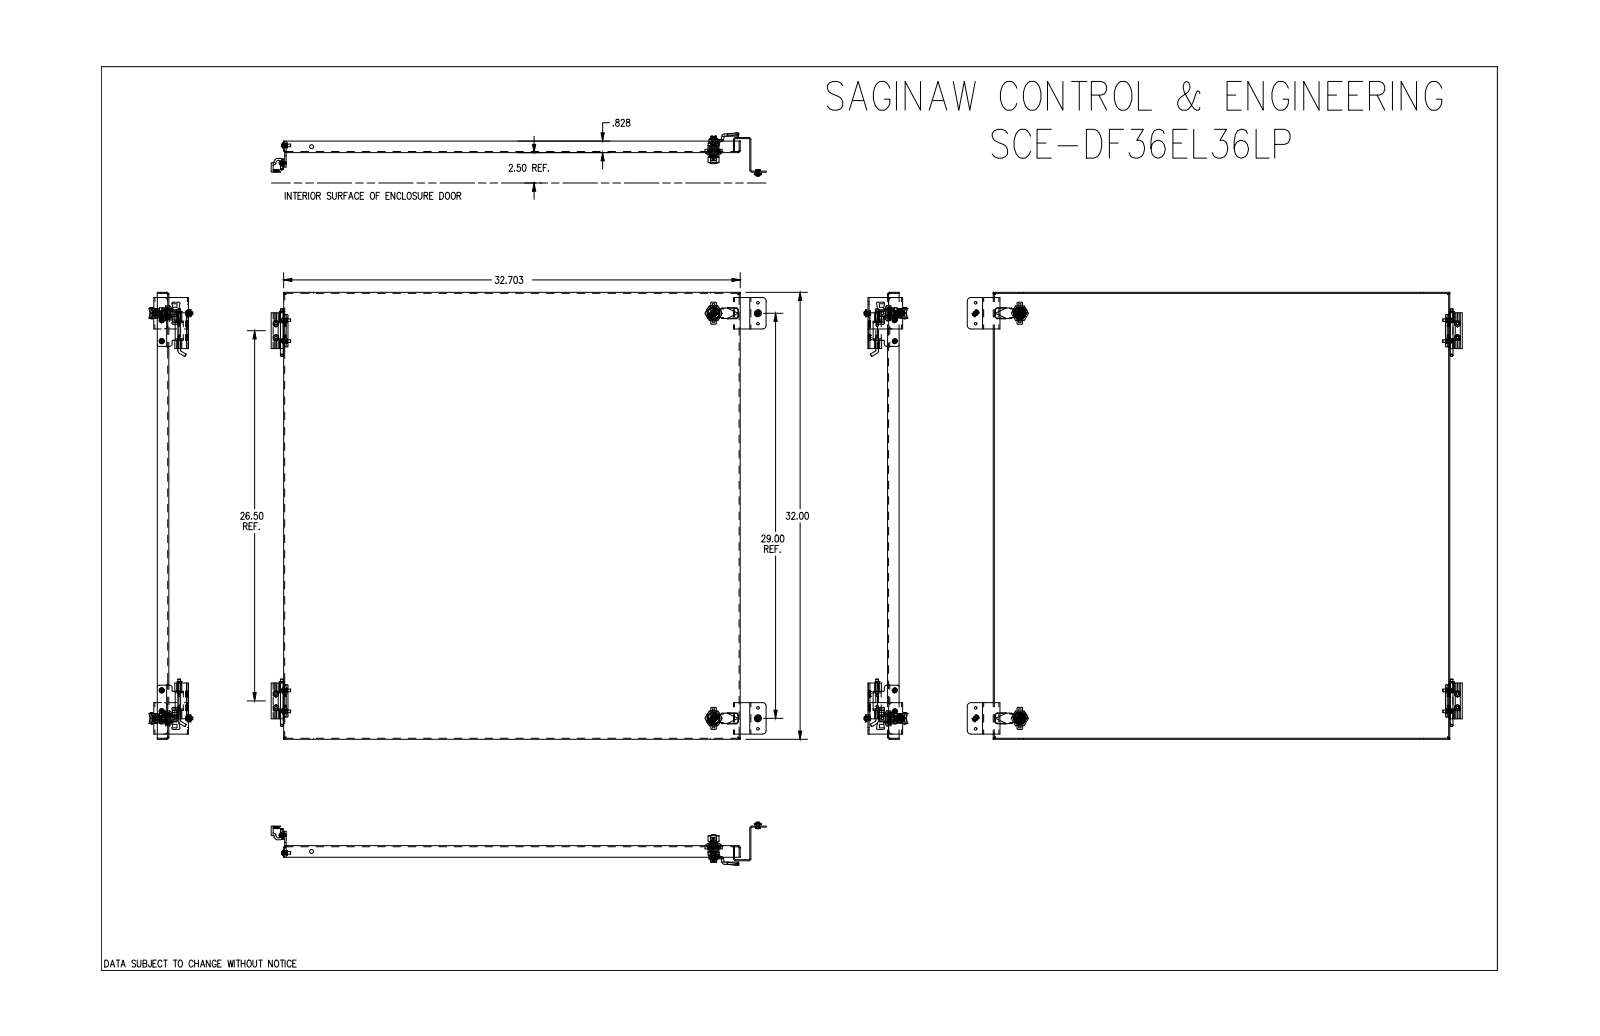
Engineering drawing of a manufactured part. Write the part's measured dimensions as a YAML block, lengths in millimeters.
part_name: "SCE-DF36EL36LP"
step_written_by: "SolidWorks 2021 (CONFIG_CONTROL_DESIGN)"
units: millimeters
bodies: {solids: 39, faces: 1125, planar: 571, cylindrical: 304, other: 250}
overall_size: [900.5, 812.8, 78.6]
volume: 1241000
surface_area: 1578000
round_holes:
  - {diameter: 4.8, count: 10}
  - {diameter: 6.4, count: 6}
  - {diameter: 4, count: 4}
  - {diameter: 4.2, count: 4}
  - {diameter: 4.8, count: 4}
  - {diameter: 5.1, count: 4}
  - {diameter: 5, count: 2}
  - {diameter: 6.3, count: 2}
  - {diameter: 10, count: 2}
  - {diameter: 11, count: 2}
  - {diameter: 16.1, count: 2}
  - {diameter: 5.3, count: 1}
round_bosses_or_shafts:
  - {diameter: 8.6, count: 6}
  - {diameter: 9.5, count: 4}
  - {diameter: 6.3, count: 4}
  - {diameter: 4.8, count: 4}
  - {diameter: 5, count: 3}
  - {diameter: 28, count: 2}
  - {diameter: 19.8, count: 2}
  - {diameter: 16, count: 2}
partial_cylinders:
  - {radius: 4, count: 16}
  - {radius: 1.5, count: 15}
  - {radius: 1.5, count: 8}
  - {radius: 2, count: 8}
  - {radius: 3.2, count: 8}
  - {radius: 6.4, count: 8}
  - {radius: 1.6, count: 5}
  - {radius: 2.6, count: 5}
face_to_face_distances: [1.5, 811.3, 1.5, 829.1, 2, 812.8, 809.8, 830.7, 827.6, 848.1]
hole_center_spacings: [673.1, 19.1, 33.2, 38.1, 43.2, 82.7, 736.6, 20]
